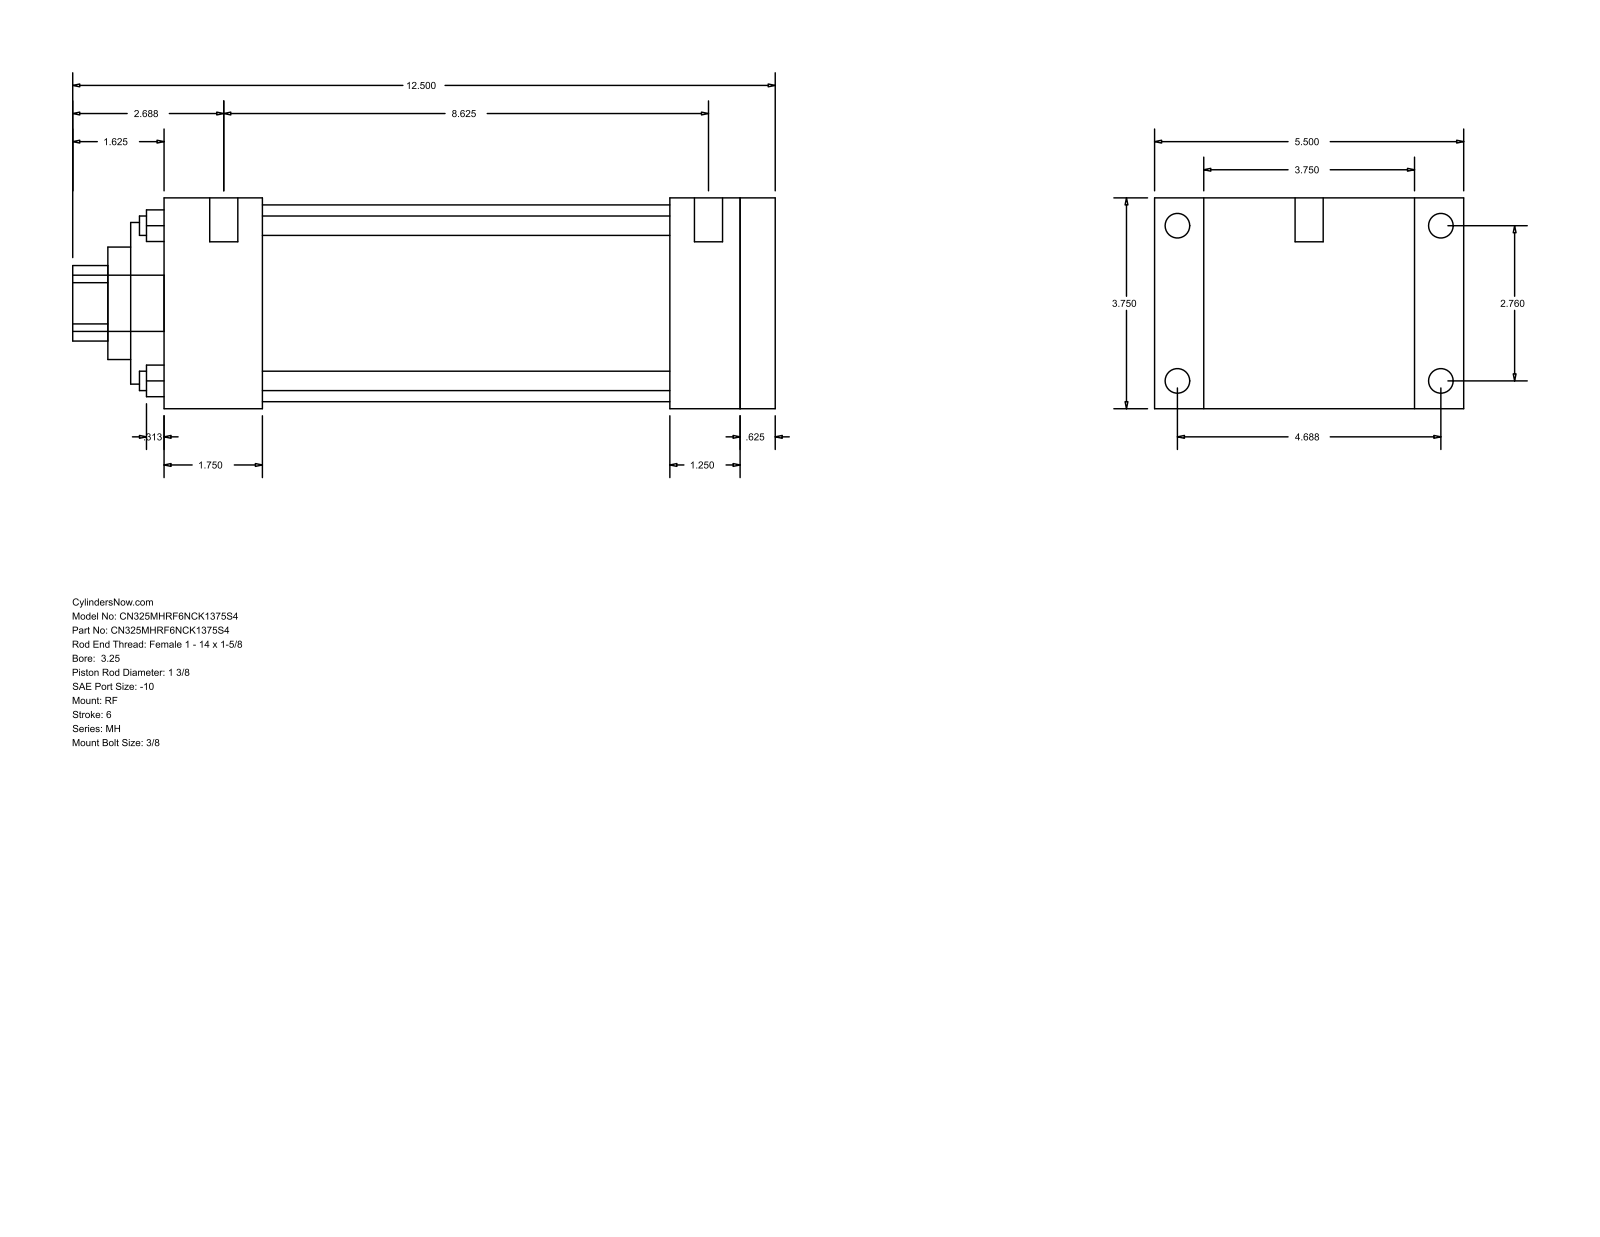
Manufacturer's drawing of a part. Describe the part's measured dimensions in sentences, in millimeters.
The part is named "MH_RF__0325_1.375". Its 3-D file was written by "GSSL Pune (CONFIG_CONTROL_DESIGN)". It is 0 solids with 94 faces: 65 planar, 29 cylindrical and 0 other. Overall it measures 317.5 by 139.7 by 95.25 millimeters. Round holes: 4 of diameter 8.76, 1 of diameter 34.92, 1 of diameter 50.8, 1 of diameter 73.03, 1 of diameter 88.9. Round bosses or shafts: 4 of diameter 11.13, 4 of diameter 5.56, 2 of diameter 12.7, 1 of diameter 25.4. Partial cylindrical surfaces (rounded edges, fillets, slot ends): 1 of radius 17.06. The main face-to-face distances are 95.24, 276.23, 15.88, 260.35, 22.23, 117.47, 44.45, 215.9, 231.78, 228.61. The hole center spacings are 49.57, 70.1, 99.14.
